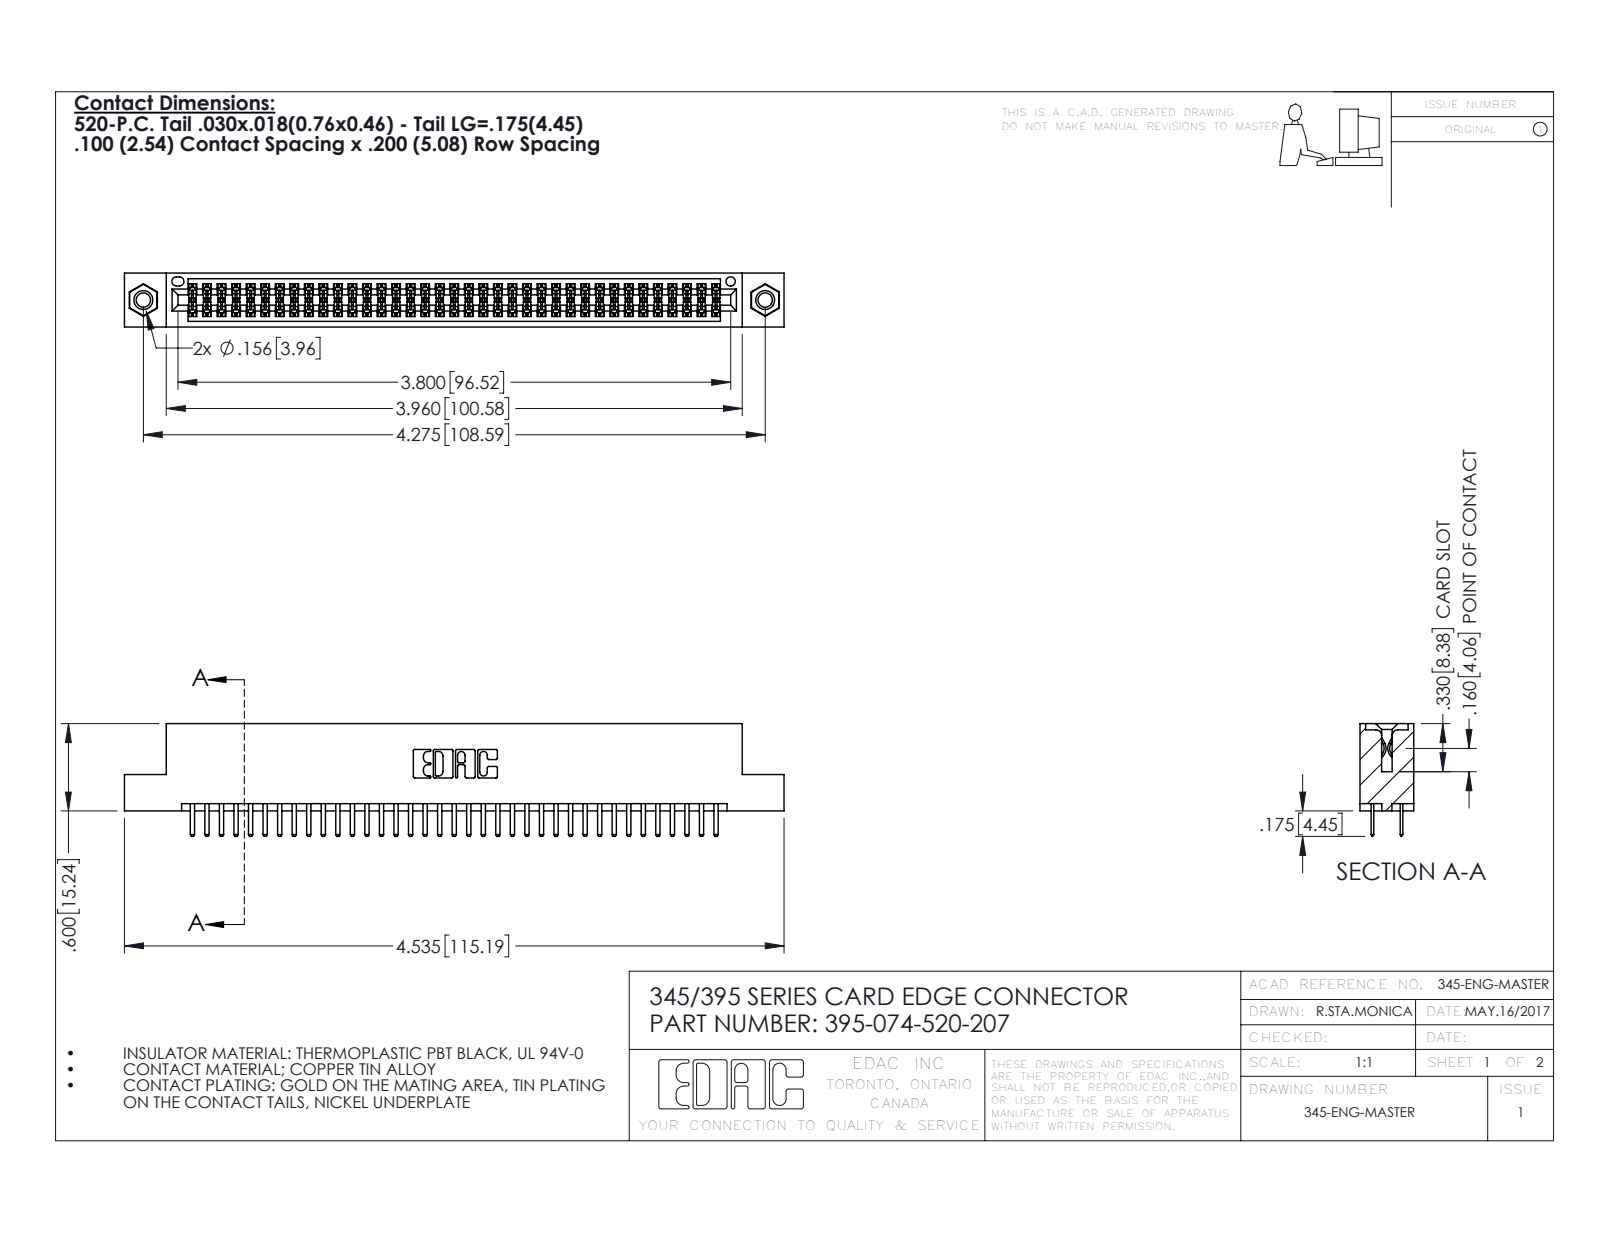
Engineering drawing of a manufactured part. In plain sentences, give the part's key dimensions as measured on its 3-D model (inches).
The part is named "345-250-001_345-250-005-103; 345 Part_Flush Mounting Lugs - 0.156 Dia-TI; 345-292-001_345-293-120; 395-074-520-207". Its 3-D file was written by "SolidWorks 2016 (CONFIG_CONTROL_DESIGN)". It is 77 solids with 4182 faces: 2702 planar, 1464 cylindrical and 16 other. Overall it measures 4.535 by 0.775 by 0.37 inches. Its volume is 0.677 cubic inches and its surface area 25.21 square inches. Round holes: 2 of diameter 0.098, 2 of diameter 0.125, 2 of diameter 0.156, 1 of diameter 0.064. Round bosses or shafts: 2 of diameter 0.155. Partial cylindrical surfaces (rounded edges, fillets, slot ends): 111 of radius 0.006, 78 of radius 0.01, 22 of radius 0.01, 6 of radius 0.007, 6 of radius 0.031, 3 of radius 0.026, 2 of radius 0.014, 2 of radius 0.019. The main face-to-face distances are 0.072, 0.298, 0.2, 0.37, 0.098, 0.272, 0.025, 0.225, 0.022, 0.072. The hole center spacings are 0.27, 4.039, 4.275.
